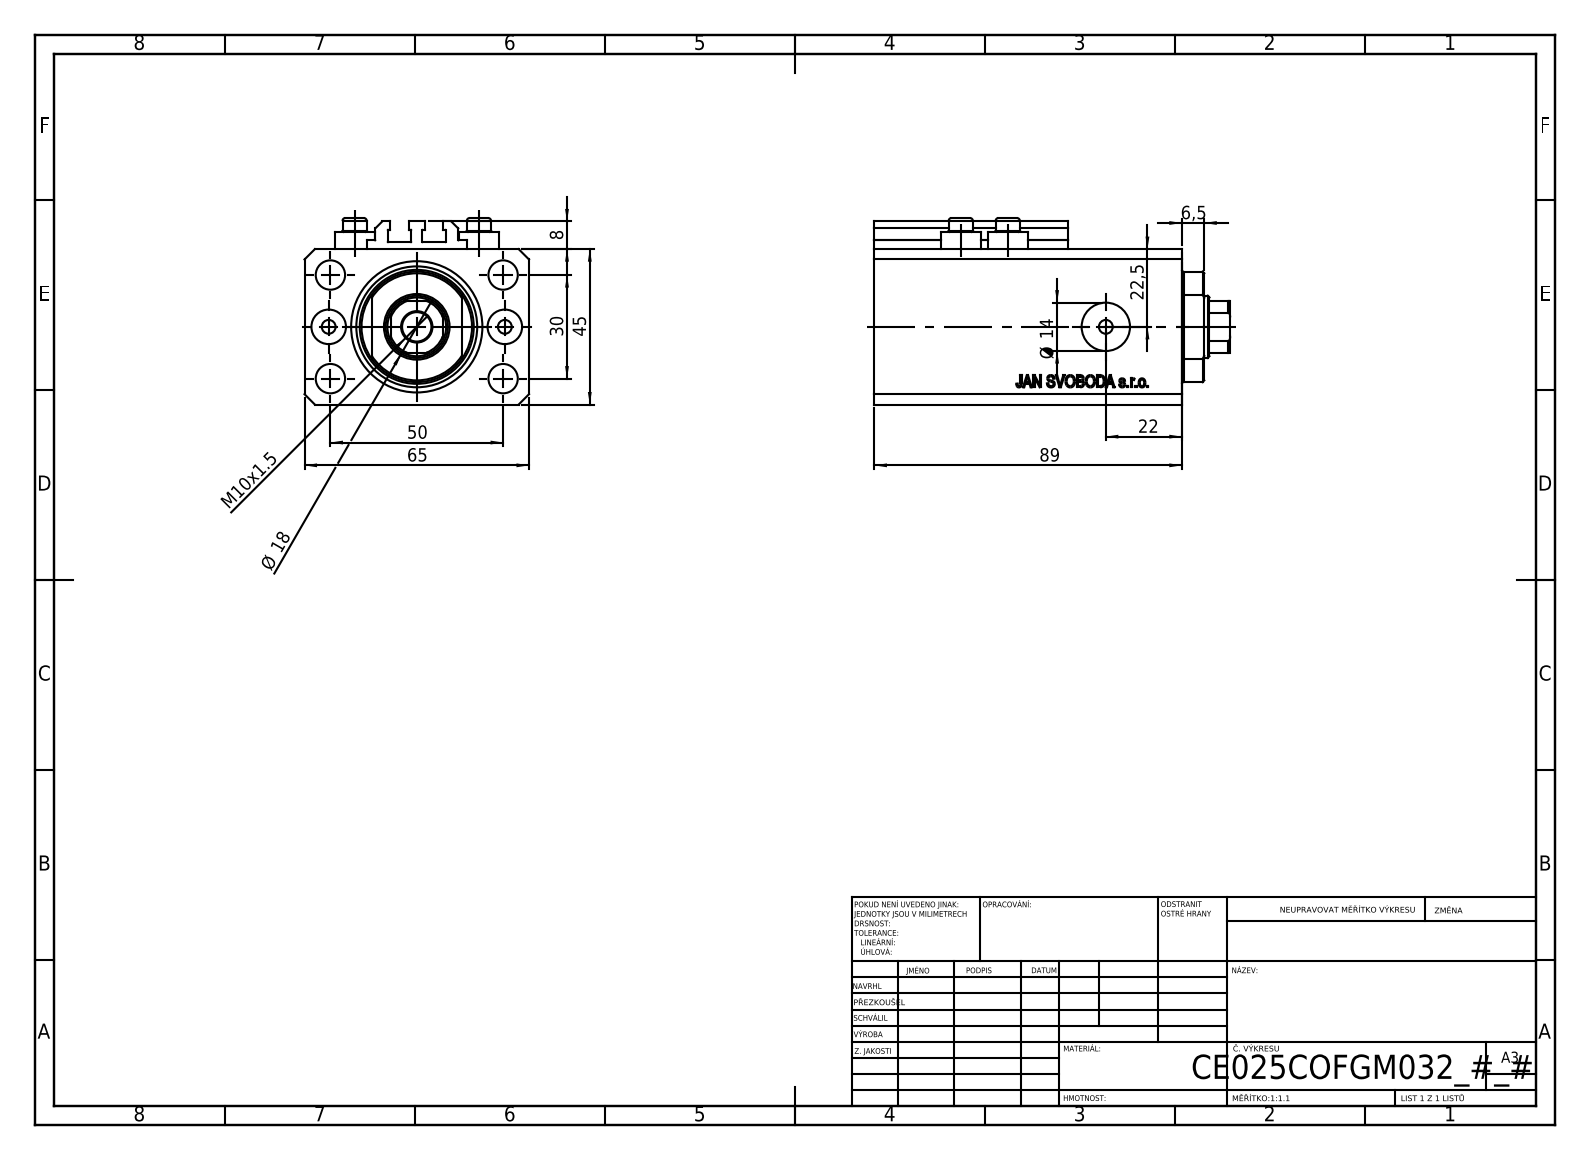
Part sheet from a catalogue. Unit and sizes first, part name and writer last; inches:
Units: inches
Overall size (bounding box): 4.055 × 2.559 × 2.126
Round holes (diameter × count): ⌀0.157 ×8, ⌀0.335 ×5, ⌀0.394 ×2, ⌀0.551 ×2, ⌀0.709 ×1, ⌀0.984 ×1, ⌀1.496 ×1
Round bosses / shafts (diameter × count): ⌀0.457 ×4, ⌀0.276 ×4
Partial cylindrical surfaces — rounded edges, fillets, slot ends (radius × count): R0.008 ×10, R0.335 ×1, R0.63 ×1
Main face-to-face distances: 1.772, 2.559, 0.551, 2.953, 3.504, 1.85, 0.272, 2.681, 3.232, 0.118
Hole centre spacings: 0.591, 1.148, 2.074, 0.535, 1.004, 1.181, 1.417, 1.515
Volume: 14.82 in³ · Surface area: 99.1 in²
Bodies: 8 solids, 1034 faces (504 planar, 86 cylindrical, 444 other)
Part name (STEP PRODUCT): V250CE_VC_C; ALLEN BOLT V250CE; V250CE_C_VCP; V250CE_C_Body
STEP written by: SolidWorks 2019 (CONFIG_CONTROL_DESIGN)
